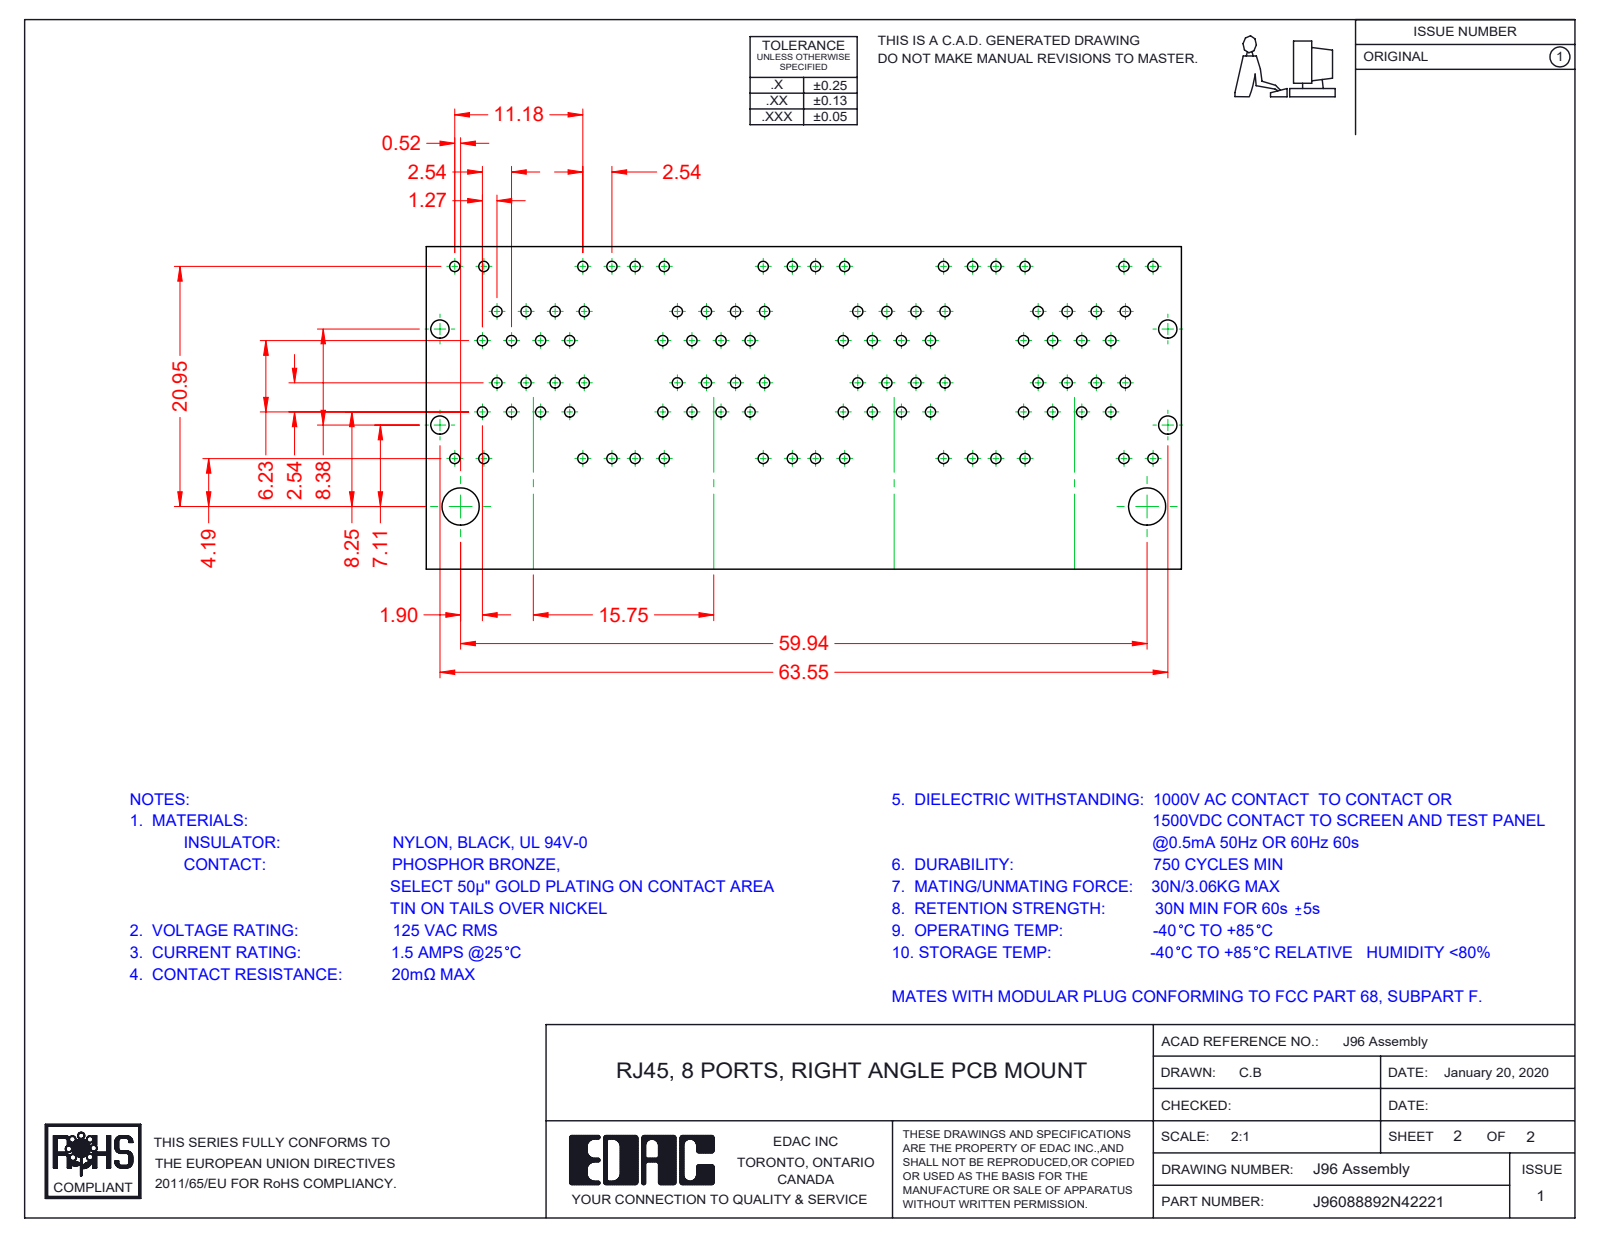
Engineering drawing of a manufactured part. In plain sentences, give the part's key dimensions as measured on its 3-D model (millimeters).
The part is named "96 Back Plate_8 Ports; 96 Insulator Insert; 96 LED RH Upper_2-Red; 96 LED RH Lower_2-Red (+8 more)". Its 3-D file was written by "SolidWorks 2016 (CONFIG_CONTROL_DESIGN)". It is 96 solids with 7804 faces: 6105 planar, 1388 cylindrical and 311 other. Overall it measures 67.35 by 31.38 by 28.68 millimeters. Its volume is 24 149 cubic millimeters and its surface area 63 596 square millimeters. Round holes: 3 of diameter 1.7. Round bosses or shafts: 3 of diameter 1.68. Partial cylindrical surfaces (rounded edges, fillets, slot ends): 124 of radius 0.25, 73 of radius 0.35, 72 of radius 1, 49 of radius 0.5, 32 of radius 0.91, 27 of radius 0.2, 14 of radius 0.27, 11 of radius 0.7. The main face-to-face distances are 15.75, 0.35, 9.95, 1.17, 1.6, 0.54, 9.98, 10.18, 12.67, 3.37. The hole center spacings are 15.75, 31.5.
